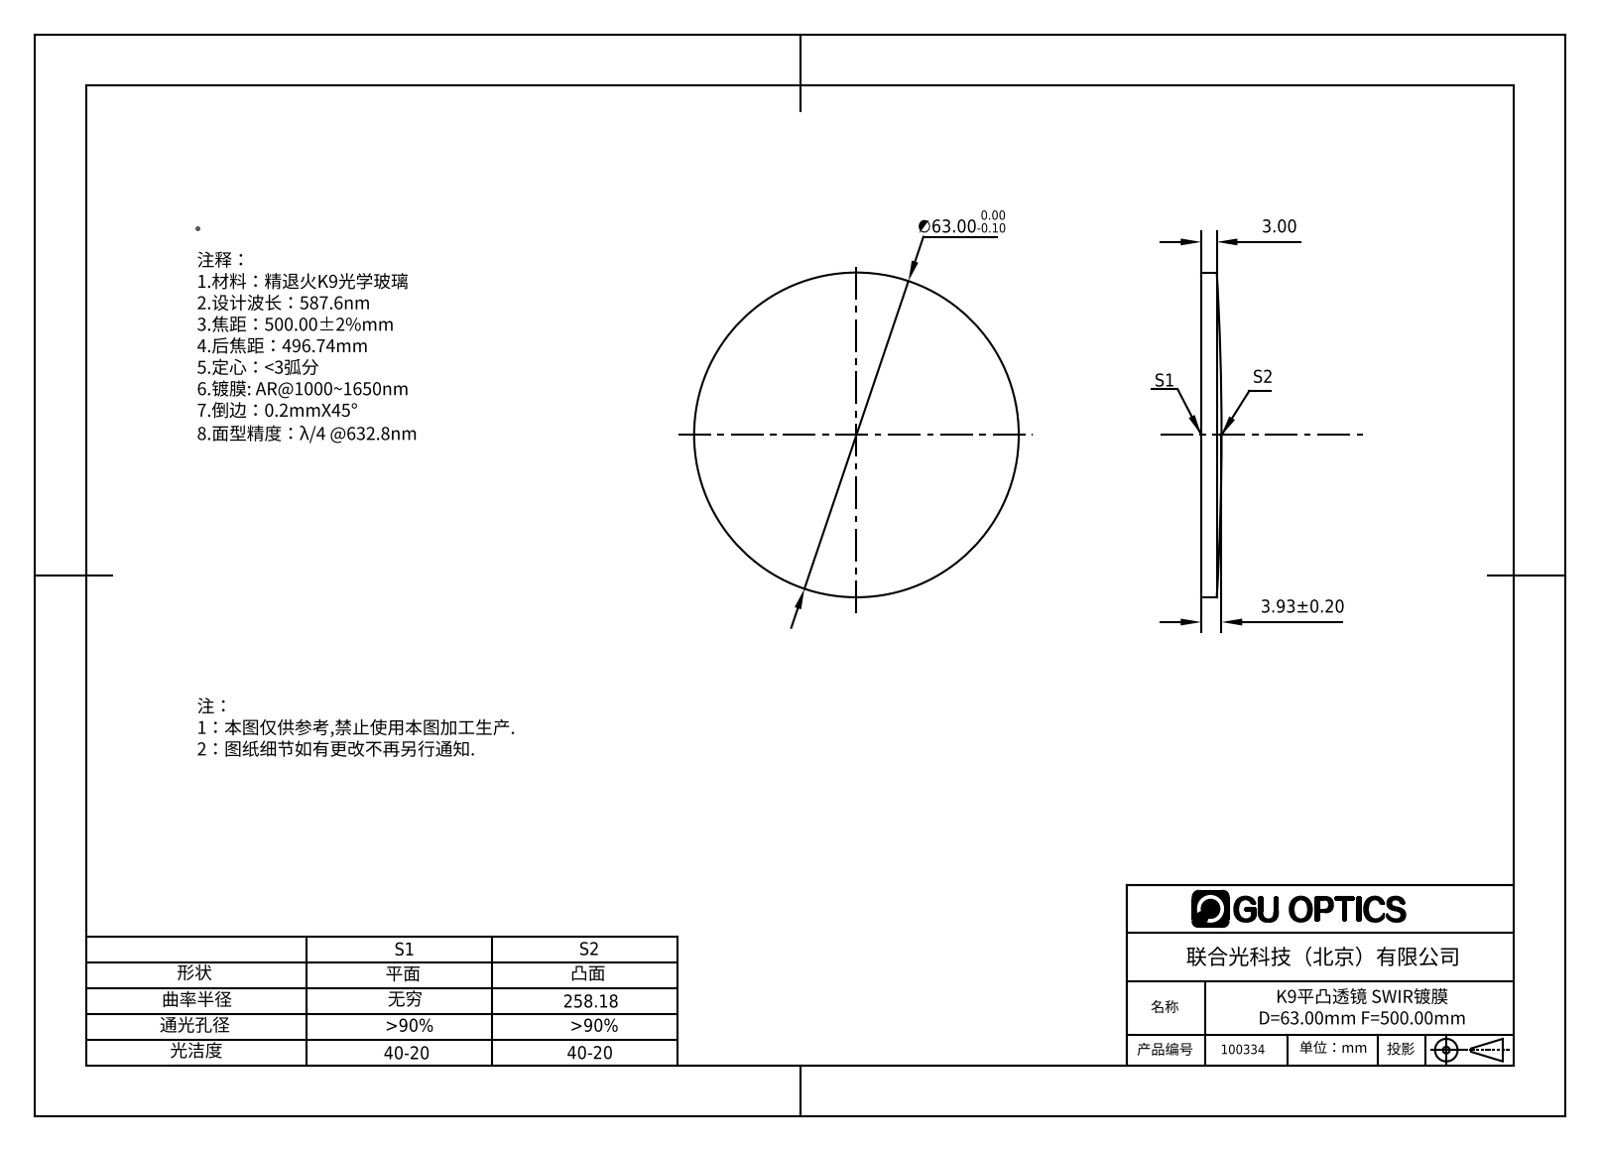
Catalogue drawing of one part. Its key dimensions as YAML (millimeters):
part_name: "100162"
step_written_by: "SolidWorks 2016 (AUTOMOTIVE_DESIGN)"
units: millimeters
bodies: {solids: 1, faces: 5, planar: 1, cylindrical: 2, other: 2}
overall_size: [63, 63, 3.93]
volume: 10802
surface_area: 6831
round_bosses_or_shafts:
  - {diameter: 63, count: 1}
